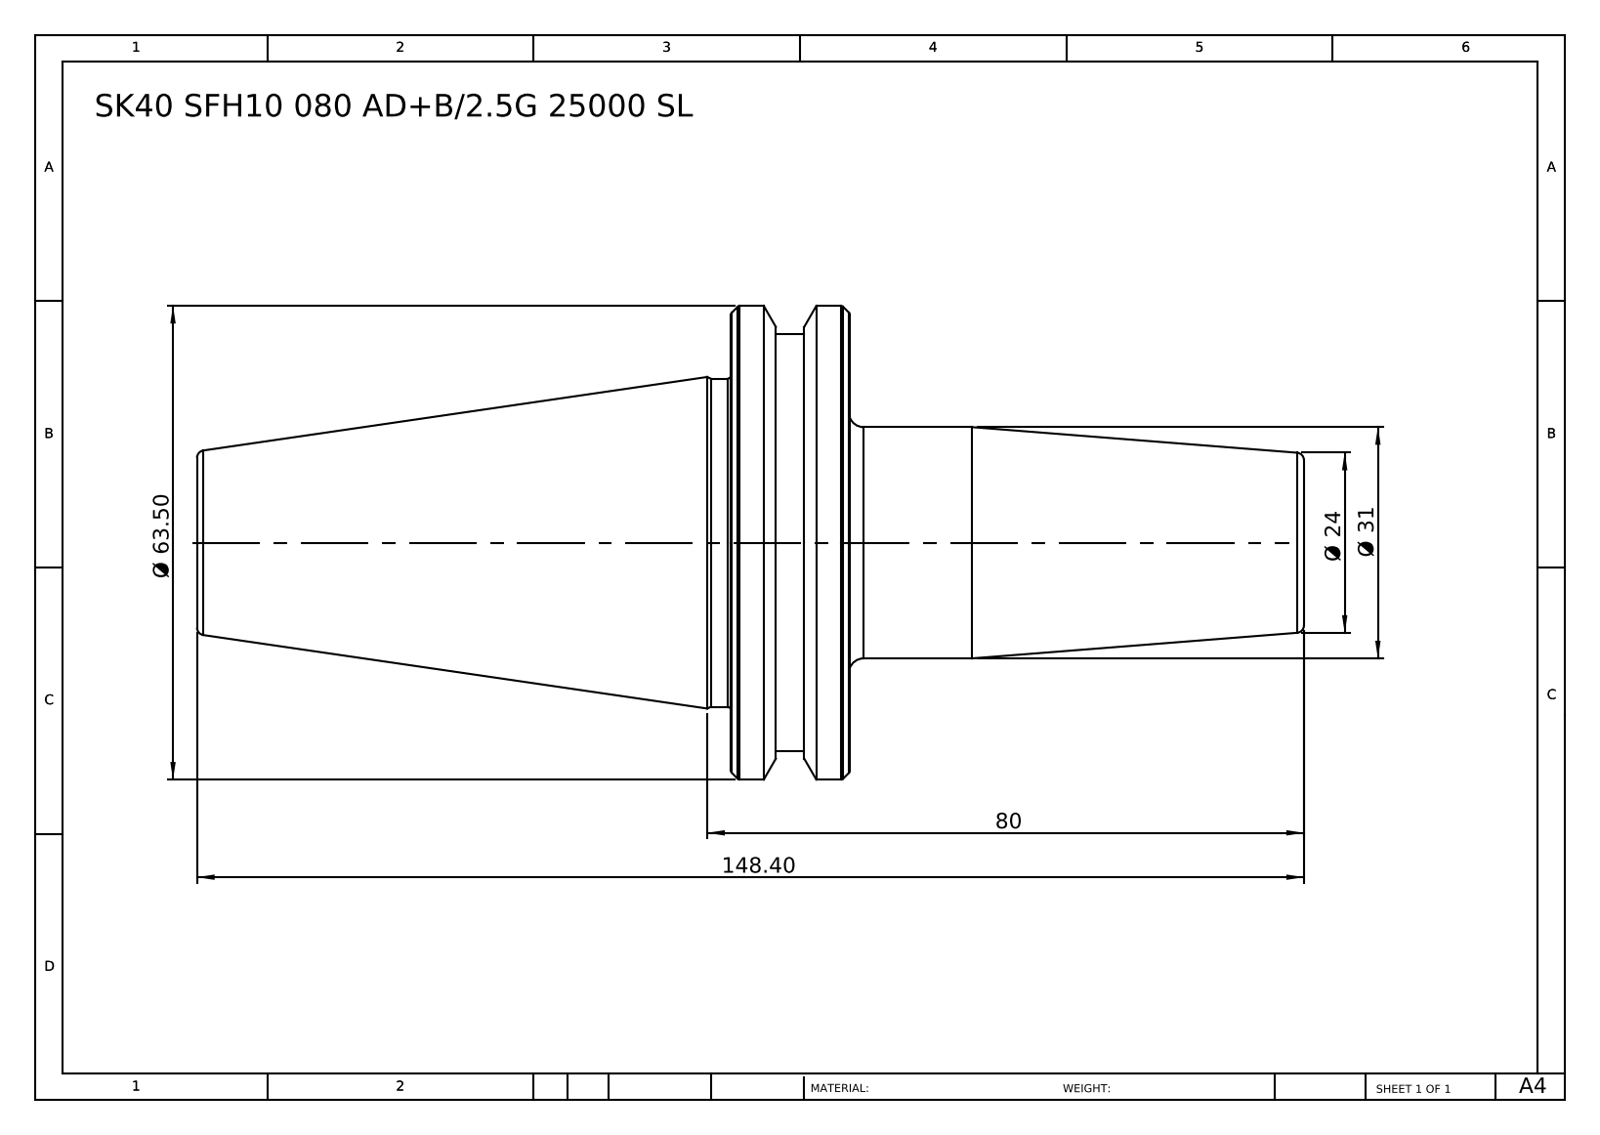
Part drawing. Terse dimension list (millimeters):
name: SK40 SFH10 80 AD+B-2.5G 25000 SL
written by: SolidWorks 2014 (CONFIG_CONTROL_DESIGN)
unit: mm
bodies: 1 solid, 46 faces (6 planar, 10 cylindrical, 30 other)
size: 148.4 × 63.5 × 63.5
volume: 156 107 mm³; area: 21 979 mm²
bosses: 1× ⌀63.5, 1× ⌀56, 1× ⌀44, 1× ⌀31
face distances: 15.9, 87.5, 71.6, 60.9, 76.8, 148.4, 67, 6.1, 9.8, 81.4
